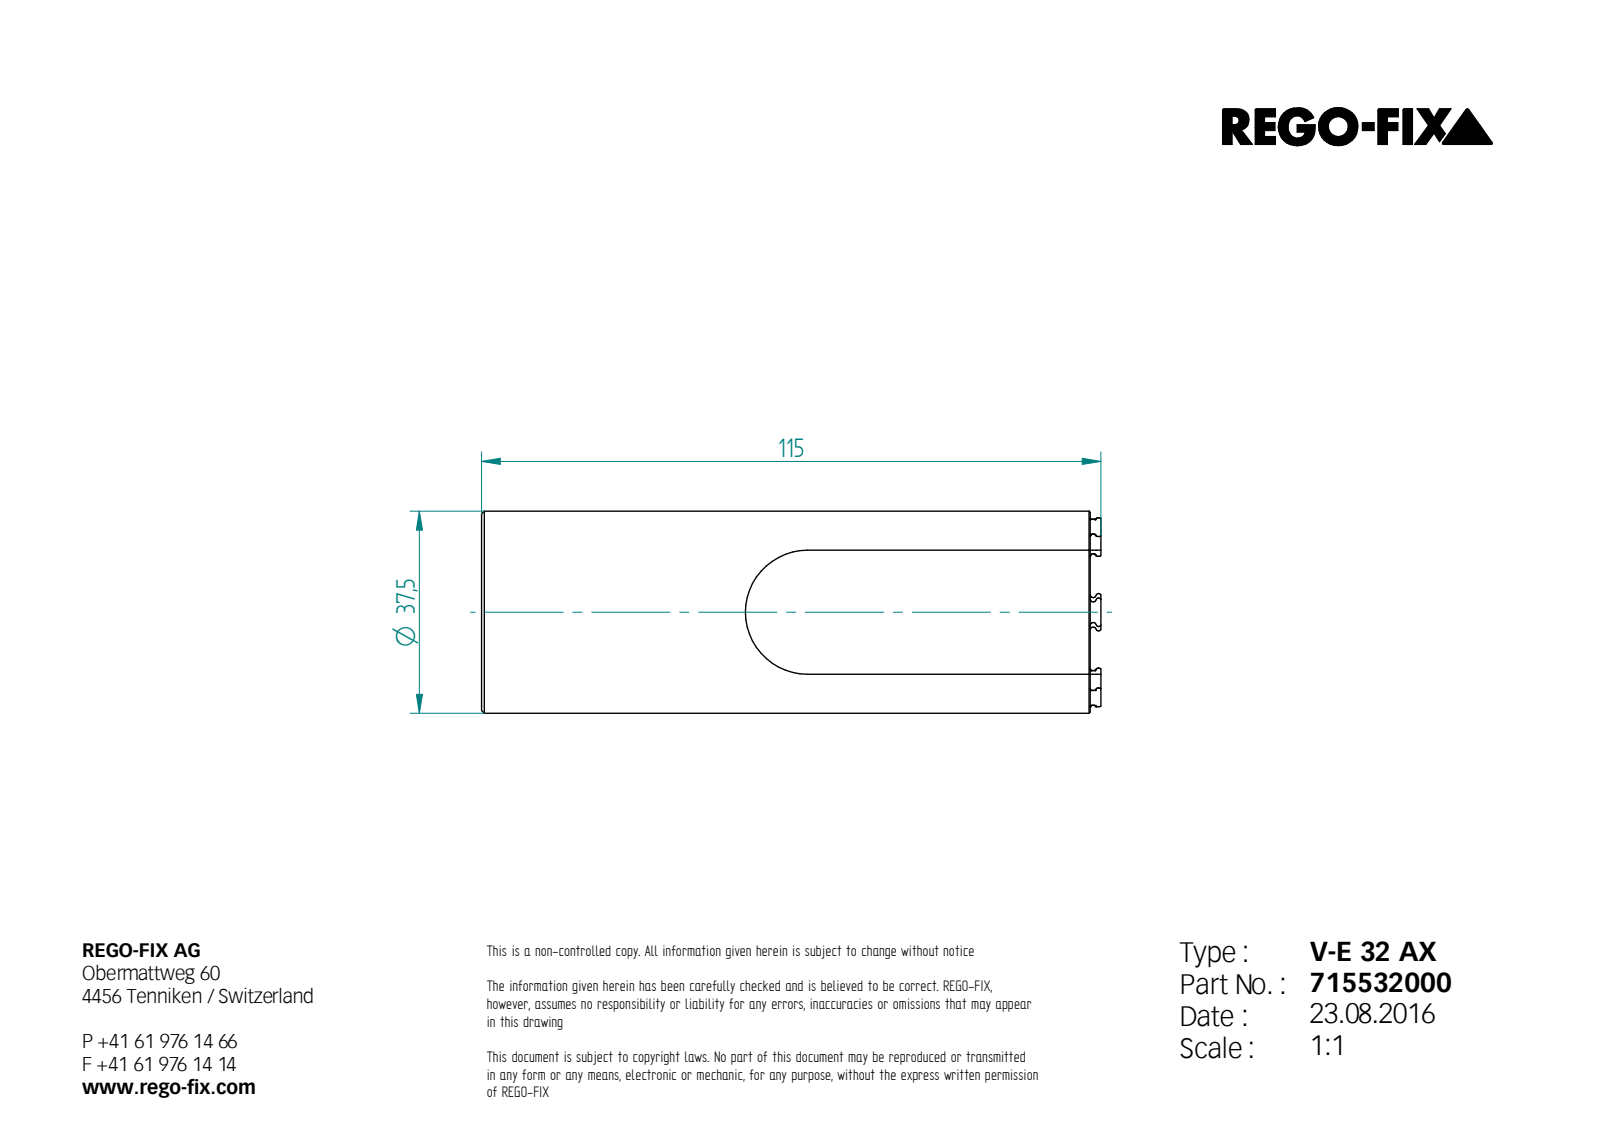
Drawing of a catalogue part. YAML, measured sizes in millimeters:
step_written_by: "Unknown (AUTOMOTIVE_DESIGN)"
units: millimeters
bodies: {solids: 1, faces: 76, planar: 26, cylindrical: 21, other: 29}
overall_size: [115, 37.5, 37.5]
volume: 61047
surface_area: 21698
round_holes:
  - {diameter: 27.1, count: 1}
round_bosses_or_shafts:
  - {diameter: 37.5, count: 1}
partial_cylinders:
  - {radius: 6.75, count: 1}
  - {radius: 11.5, count: 1}
  - {radius: 13.75, count: 1}
  - {radius: 18.55, count: 1}
face_to_face_distances: [23, 5.05, 17.95, 12.9, 113, 115, 2, 17.4]
